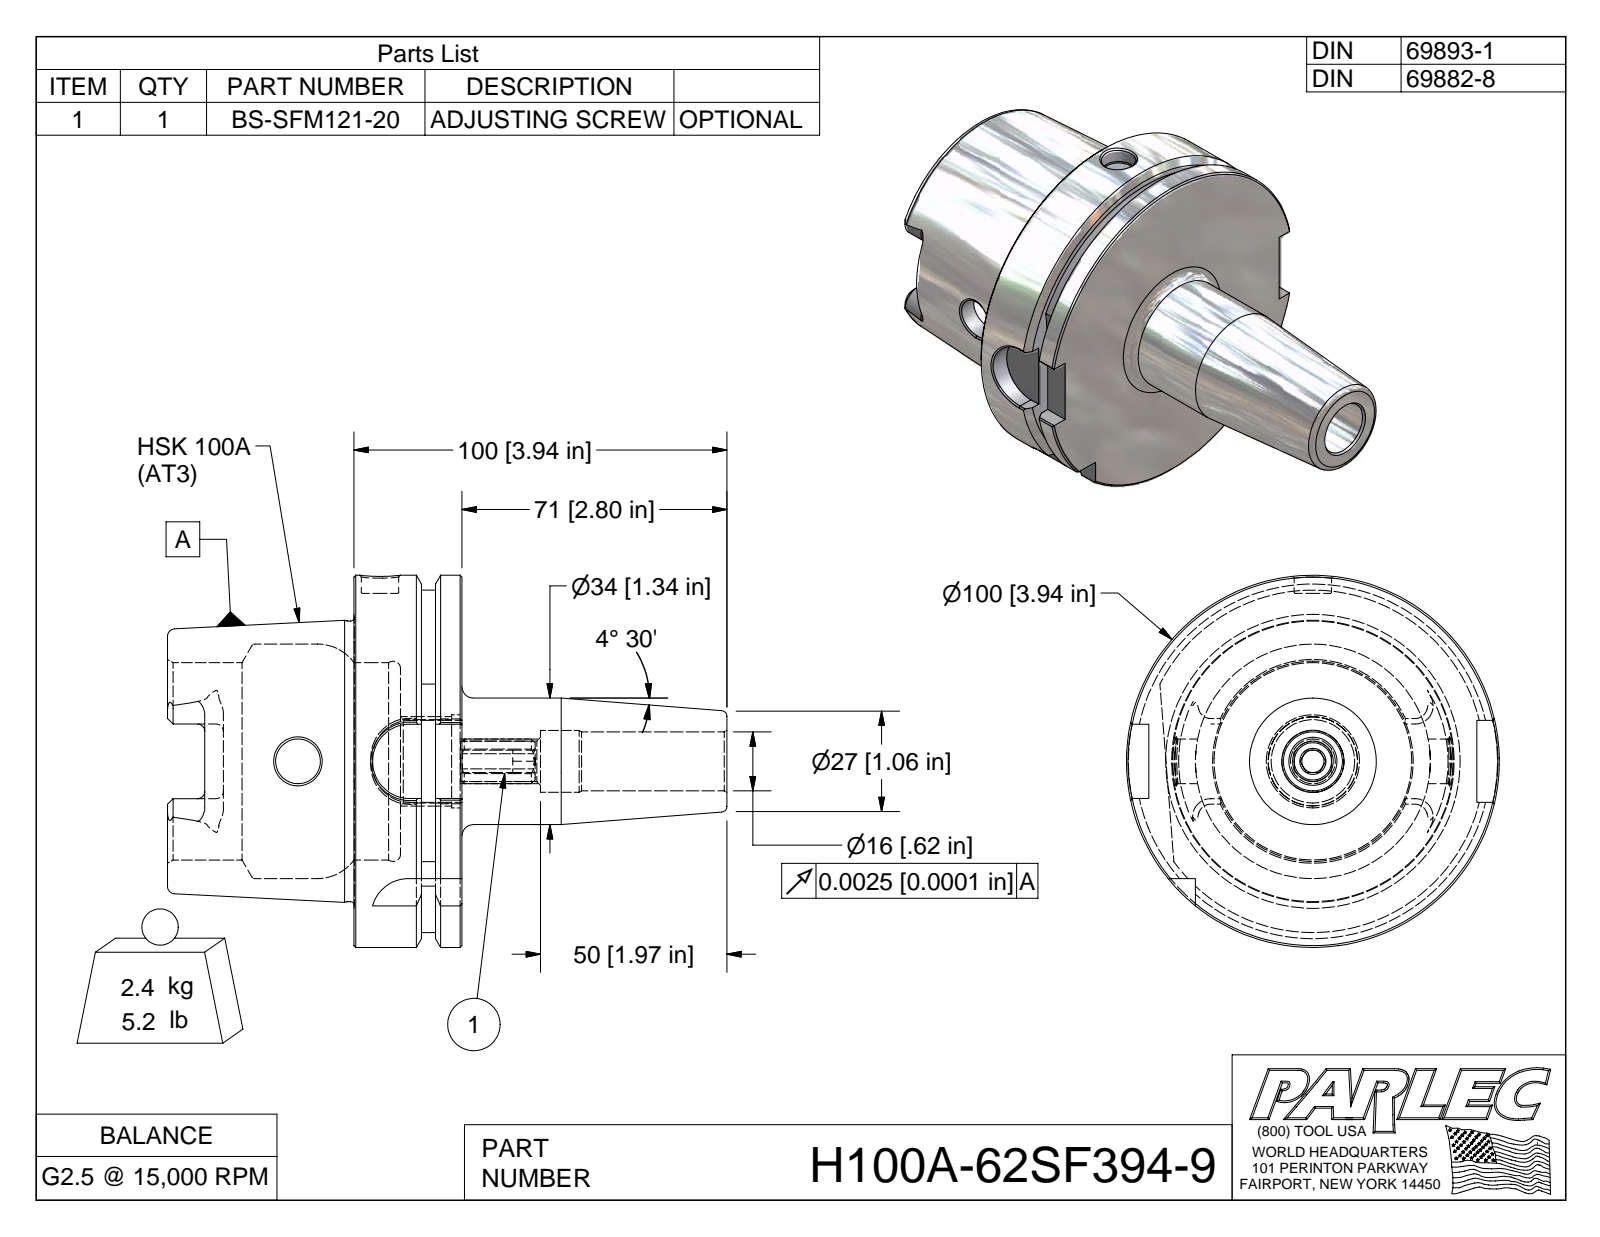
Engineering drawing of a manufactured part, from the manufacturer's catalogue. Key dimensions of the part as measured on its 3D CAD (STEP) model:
Part name (STEP PRODUCT): H100A-62SF394-9; H100A-62SF394-9-1; BS-SFM121-20
STEP written by: Autodesk Inventor 2009 (AUTOMOTIVE_DESIGN)
Units: inches
Bodies: 2 solids, 147 faces (49 planar, 30 cylindrical, 68 other)
Overall size (bounding box): 5.909 × 3.937 × 3.937
Volume: 18.31 in³ · Surface area: 94.49 in²
Round holes (diameter × count): ⌀0.394 ×1, ⌀0.472 ×1, ⌀0.624 ×1, ⌀0.654 ×1, ⌀0.881 ×1, ⌀0.985 ×1, ⌀2.087 ×1, ⌀2.48 ×1
Round bosses / shafts (diameter × count): ⌀3.937 ×1, ⌀2.967 ×1, ⌀1.339 ×1
Partial cylindrical surfaces — rounded edges, fillets, slot ends (radius × count): R0.394 ×4, R0.079 ×3, R0.192 ×2, R0.236 ×1, R1.811 ×1
Main face-to-face distances: 1.142, 0.492, 0.65, 1.969, 2.461, 3.11, 2.682, 0.713, 0.221, 0.428
